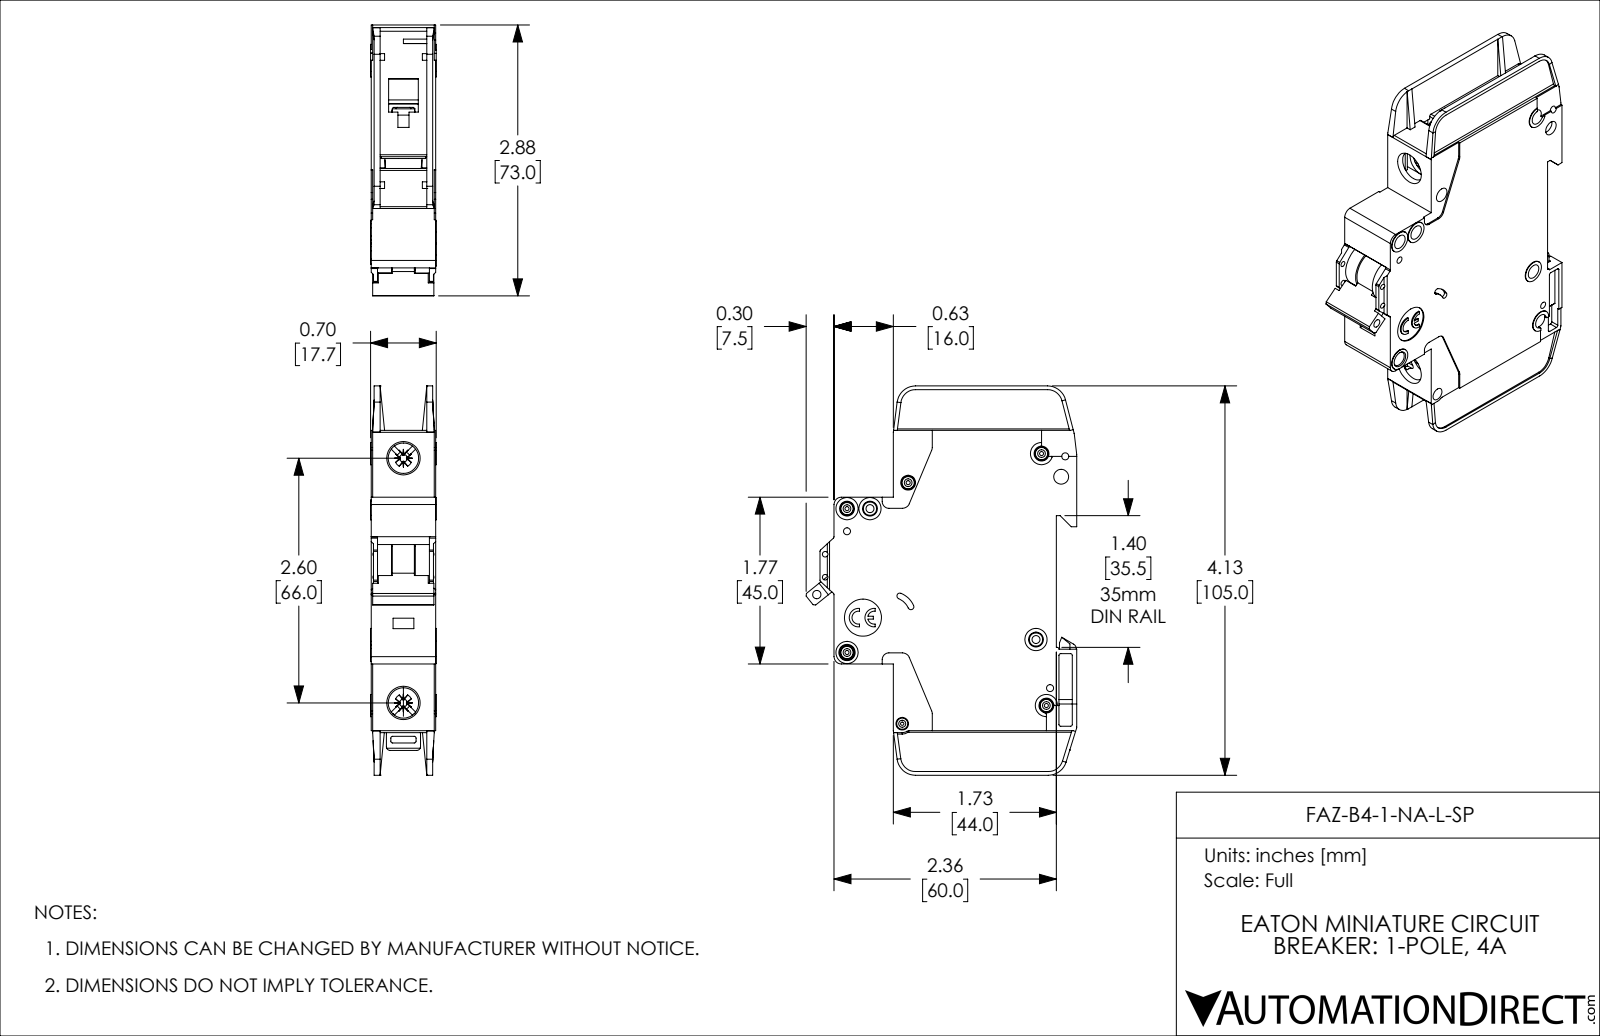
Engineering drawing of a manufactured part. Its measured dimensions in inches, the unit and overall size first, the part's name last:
Units: inches
Overall size (bounding box): 4.134 × 2.876 × 0.697
Round holes (diameter × count): ⌀0.157 ×8, ⌀0.043 ×5, ⌀0.075 ×4, ⌀0.059 ×2, ⌀0.085 ×2, ⌀0.323 ×2, ⌀0.035 ×1, ⌀0.089 ×1, ⌀0.098 ×1, ⌀0.134 ×1, ⌀0.394 ×1
Round bosses / shafts (diameter × count): ⌀0.13 ×5, ⌀0.236 ×4, ⌀0.118 ×2, ⌀0.098 ×1
Partial cylindrical surfaces — rounded edges, fillets, slot ends (radius × count): R0.02 ×42, R0.016 ×10, R0.039 ×10, R0.079 ×8, R0.197 ×5, R0.008 ×4, R0.026 ×4, R0.043 ×4
Main face-to-face distances: 0.047, 0.685, 0.591, 0.638, 0.094, 0.543, 0.016, 0.031, 0.496, 0.575
Hole centre spacings: 0.244, 0.537, 0.87, 0.189, 0.199, 0.204, 0.221, 0.24
Volume: 4.682 in³ · Surface area: 41.01 in²
Bodies: 1 solid, 1127 faces (671 planar, 357 cylindrical, 99 other)
Part name (STEP PRODUCT): FAZ-B4-1-NA-L-SP
STEP written by: SolidWorks 2019 (AUTOMOTIVE_DESIGN)
